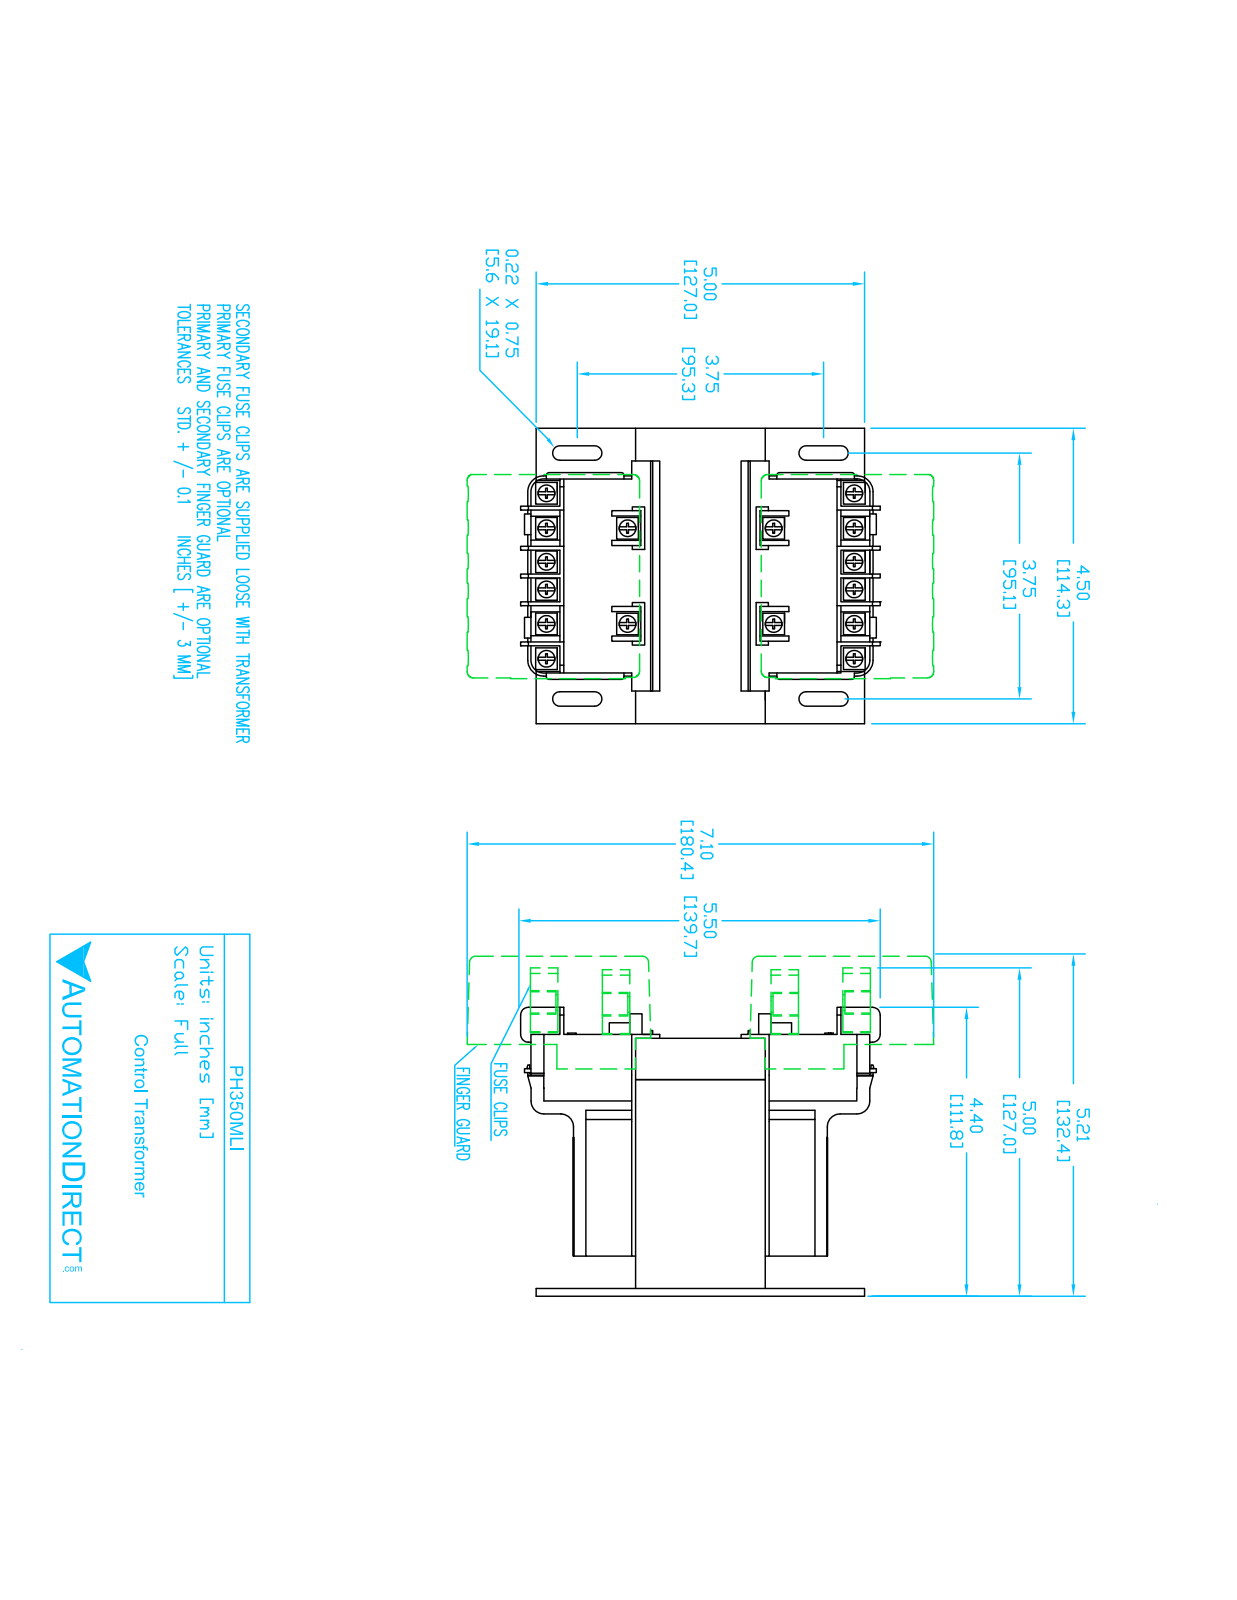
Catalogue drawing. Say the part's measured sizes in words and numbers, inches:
The part is named "PH350MLI". Its 3-D file was written by "SolidWorks 2017 (AUTOMOTIVE_DESIGN)". It is 8 solids with 646 faces: 374 planar, 192 cylindrical and 80 other. Overall it measures 5.469 by 4.5 by 4.331 inches. Its volume is 68.86 cubic inches and its surface area 225 square inches. Round holes: 8 of diameter 0.157. Partial cylindrical surfaces (rounded edges, fillets, slot ends): 90 of radius 0.039, 18 of radius 0.197, 8 of radius 0.11, 4 of radius 0.1, 4 of radius 0.243. The main face-to-face distances are 1.969, 3.858, 0.187, 2.992, 3.179, 0.63, 4.213, 1.22, 1.033, 0.472. The hole center spacings are 3.75, 3.991, 0.383, 1.367, 3.769, 0.984, 3.877, 4.138.
